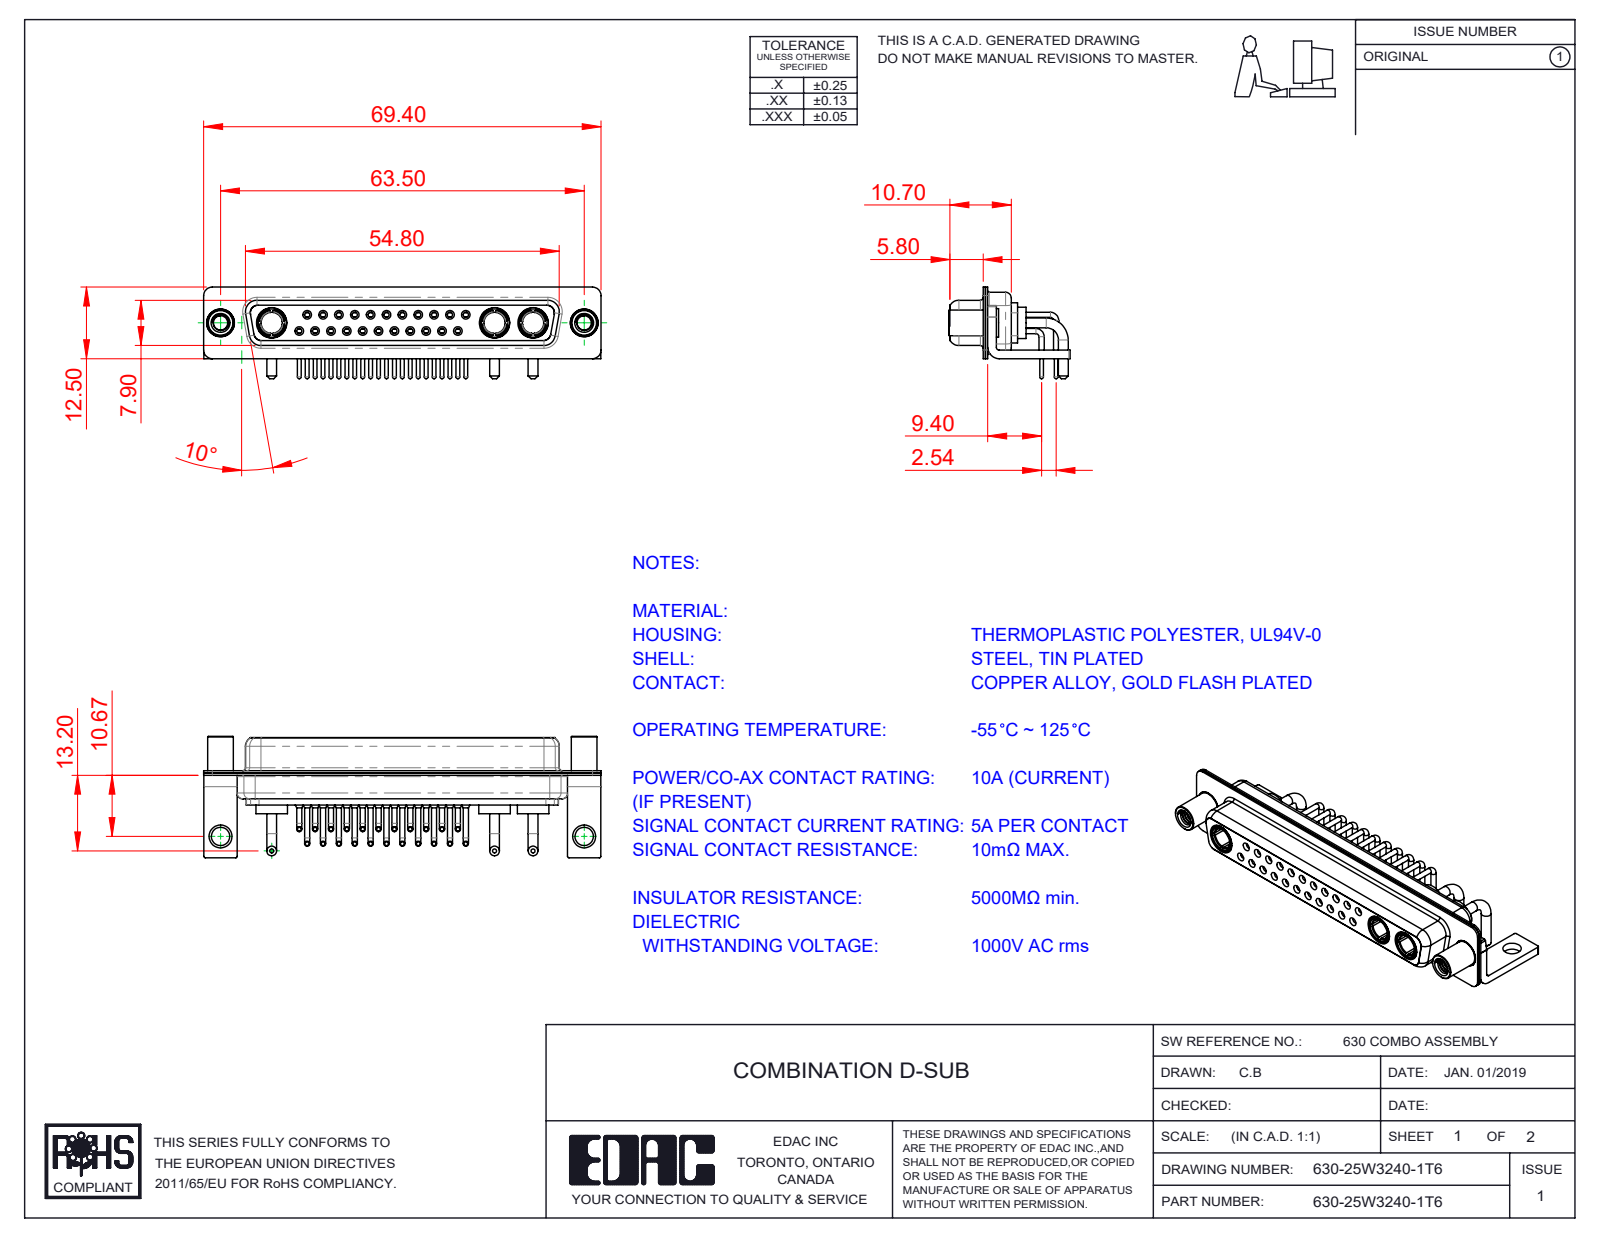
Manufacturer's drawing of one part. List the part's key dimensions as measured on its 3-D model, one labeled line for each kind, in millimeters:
Part name (STEP PRODUCT): 630Combo Shell Rear_37 Contacts; 630Combo Contact Row 2; 630Combo Shell Front_37 Contacts; 630Combo Threaded Standoff_D (+5 more)
STEP written by: SolidWorks 2020 (CONFIG_CONTROL_DESIGN)
Units: millimetres
Bodies: 35 solids, 1777 faces (506 planar, 790 cylindrical, 481 other)
Overall size (bounding box): 69.4 × 21.2 × 16
Volume: 5 886 mm³ · Surface area: 13 488 mm²
Round holes (diameter × count): ⌀0.9 ×22, ⌀1.1 ×22, ⌀1.5 ×22, ⌀2 ×22, ⌀1.6 ×11, ⌀1.7 ×11, ⌀4.85 ×5, ⌀3.7 ×3, ⌀5.3 ×3, ⌀2.5 ×2, ⌀3.2 ×2, ⌀4 ×2
Round bosses / shafts (diameter × count): ⌀0.9 ×23, ⌀0.65 ×22, ⌀1.6 ×12, ⌀1.7 ×6, ⌀5.5 ×3, ⌀5.2 ×3, ⌀4.96 ×3, ⌀4.75 ×3
Partial cylindrical surfaces — rounded edges, fillets, slot ends (radius × count): R0.25 ×16, R1.5 ×16, R2 ×13, R1.35 ×8, R1.6 ×8, R0.5 ×5, R0.6 ×4, R0.65 ×4
Main face-to-face distances: 0.4, 0.45, 1.4, 8.45, 1.8, 8.9, 6.2, 7.05, 0.8, 7.5
Hole centre spacings: 3.16, 2.77, 5.54, 5.03, 8.31, 7.48, 11.08, 5.04
